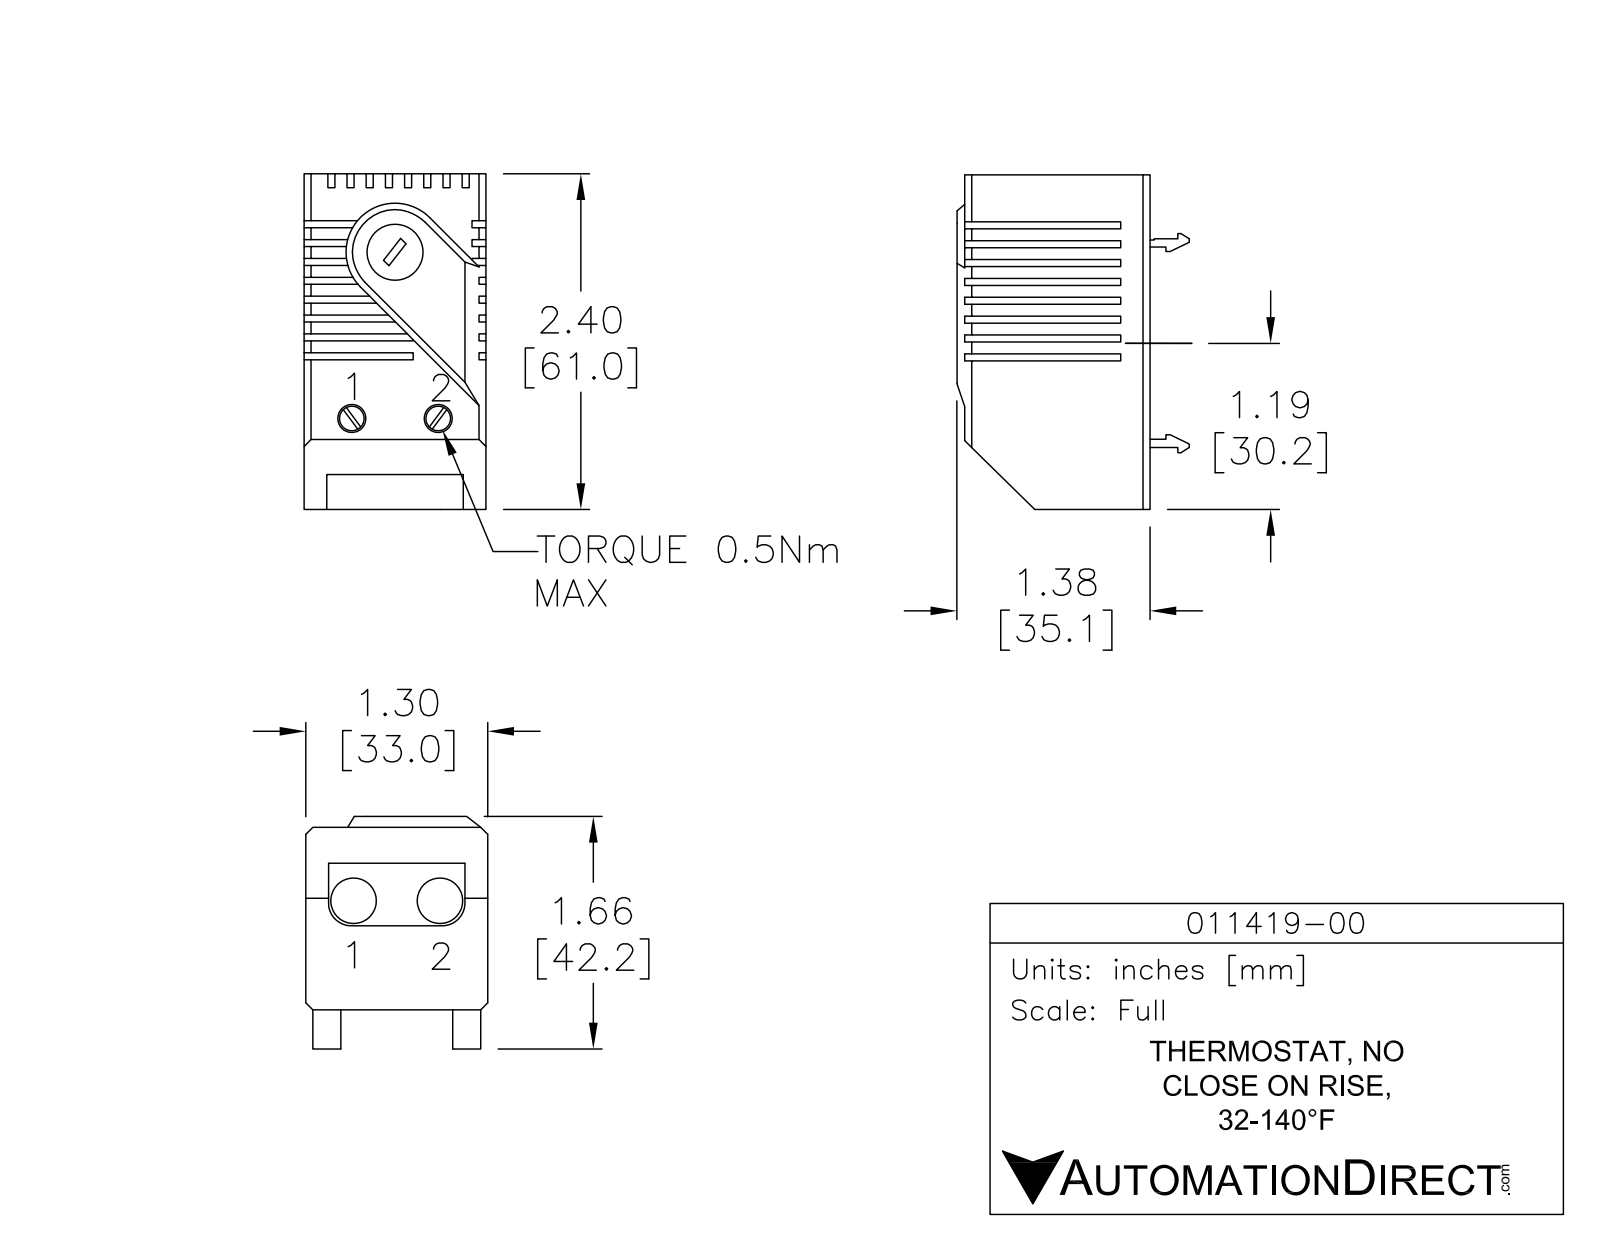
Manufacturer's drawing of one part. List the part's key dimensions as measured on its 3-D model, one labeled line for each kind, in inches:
Part name (STEP PRODUCT): 011419-00
STEP written by: SolidWorks 2013 (AUTOMOTIVE_DESIGN)
Units: inches
Bodies: 1 solid, 424 faces (392 planar, 18 cylindrical, 14 other)
Overall size (bounding box): 2.358 × 1.67 × 1.303
Volume: 3.565 in³ · Surface area: 28.9 in²
Round holes (diameter × count): ⌀0.12 ×2, ⌀0.245 ×2
Round bosses / shafts (diameter × count): ⌀0.38 ×1, ⌀0.3 ×1, ⌀0.294 ×1
Partial cylindrical surfaces — rounded edges, fillets, slot ends (radius × count): R0.55 ×2, R0.15 ×1
Main face-to-face distances: 0.18, 0.09, 0.27, 0.45, 0.05, 0.36, 0.4, 0.04, 0.13, 0.09
Hole centre spacings: 0.41
